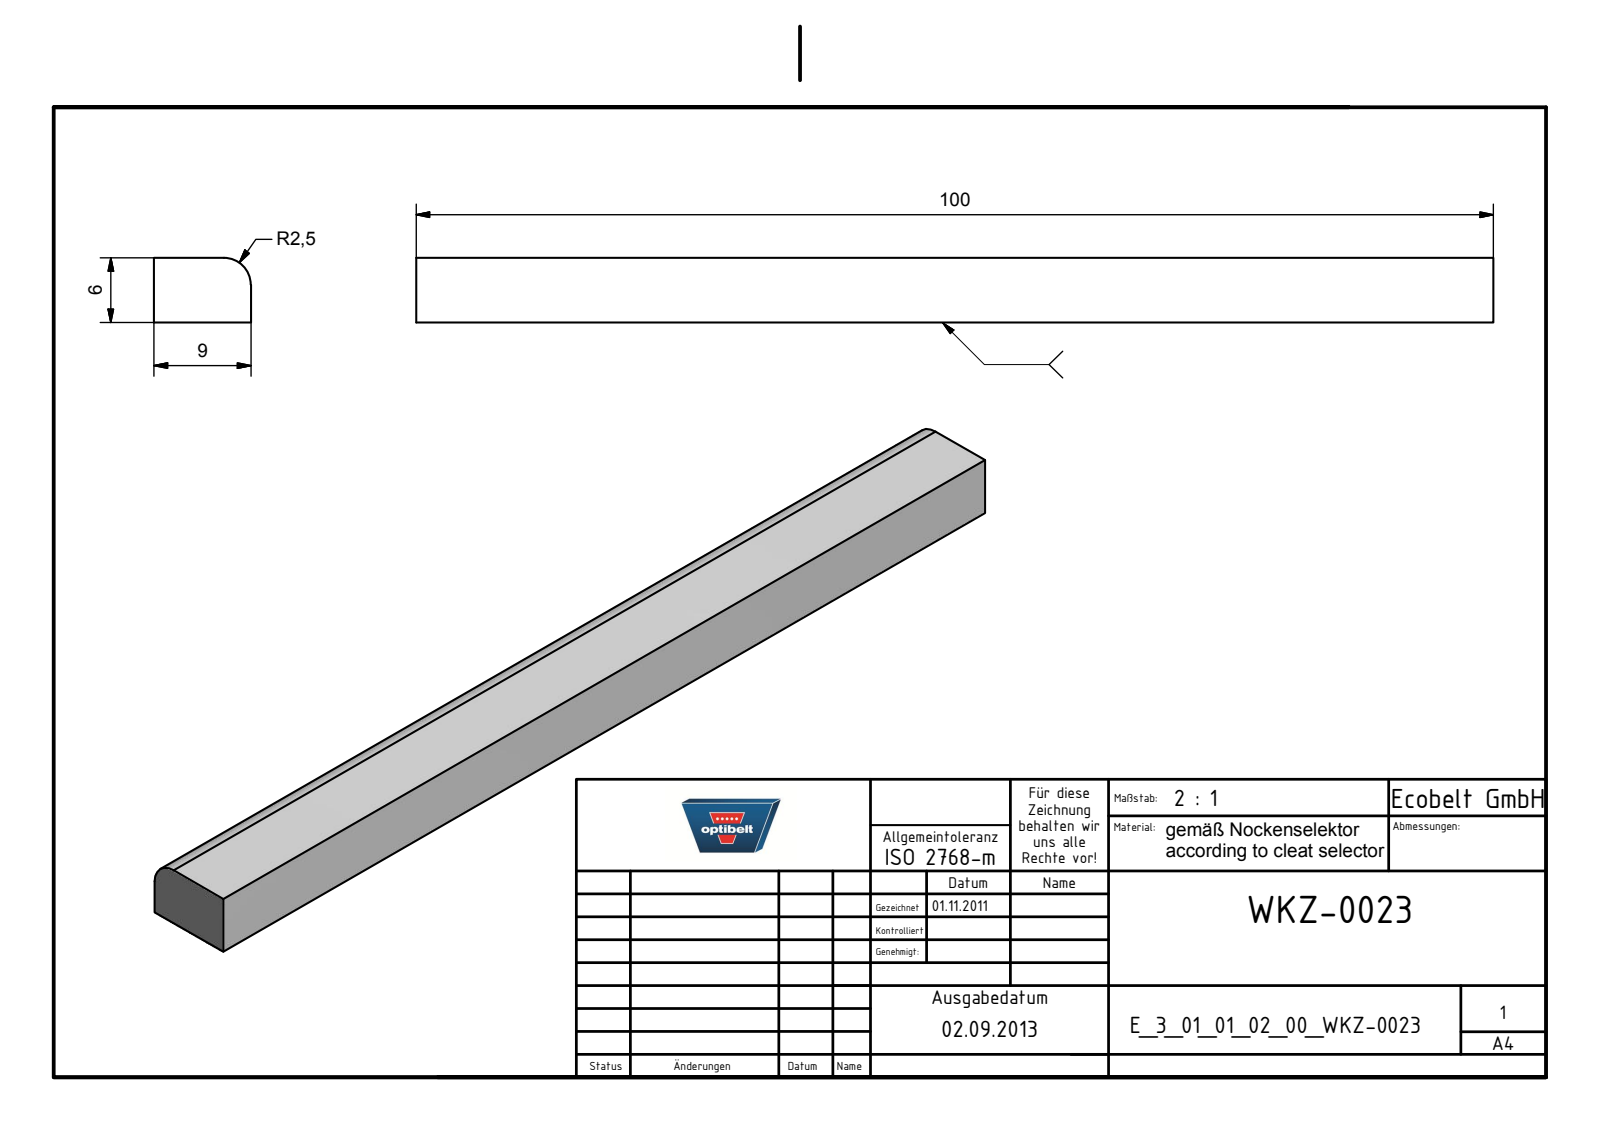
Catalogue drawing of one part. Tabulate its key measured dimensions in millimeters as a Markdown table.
| quantity | value |
| --- | --- |
| part name | E_3_01_01_02_00_WKZ-0023 |
| STEP written by | Autodesk Inventor 2021 (AUTOMOTIVE_DESIGN) |
| units | millimeters |
| bodies | 1 solid, 7 faces (6 planar, 1 cylindrical, 0 other) |
| overall size | 100 × 9 × 6 |
| volume | 5 266 mm³ |
| surface area | 2 998 mm² |
| partial cylindrical surfaces (radius × count) | 2.5 × 1 |
| main face-to-face distances | 6, 9, 100 |
